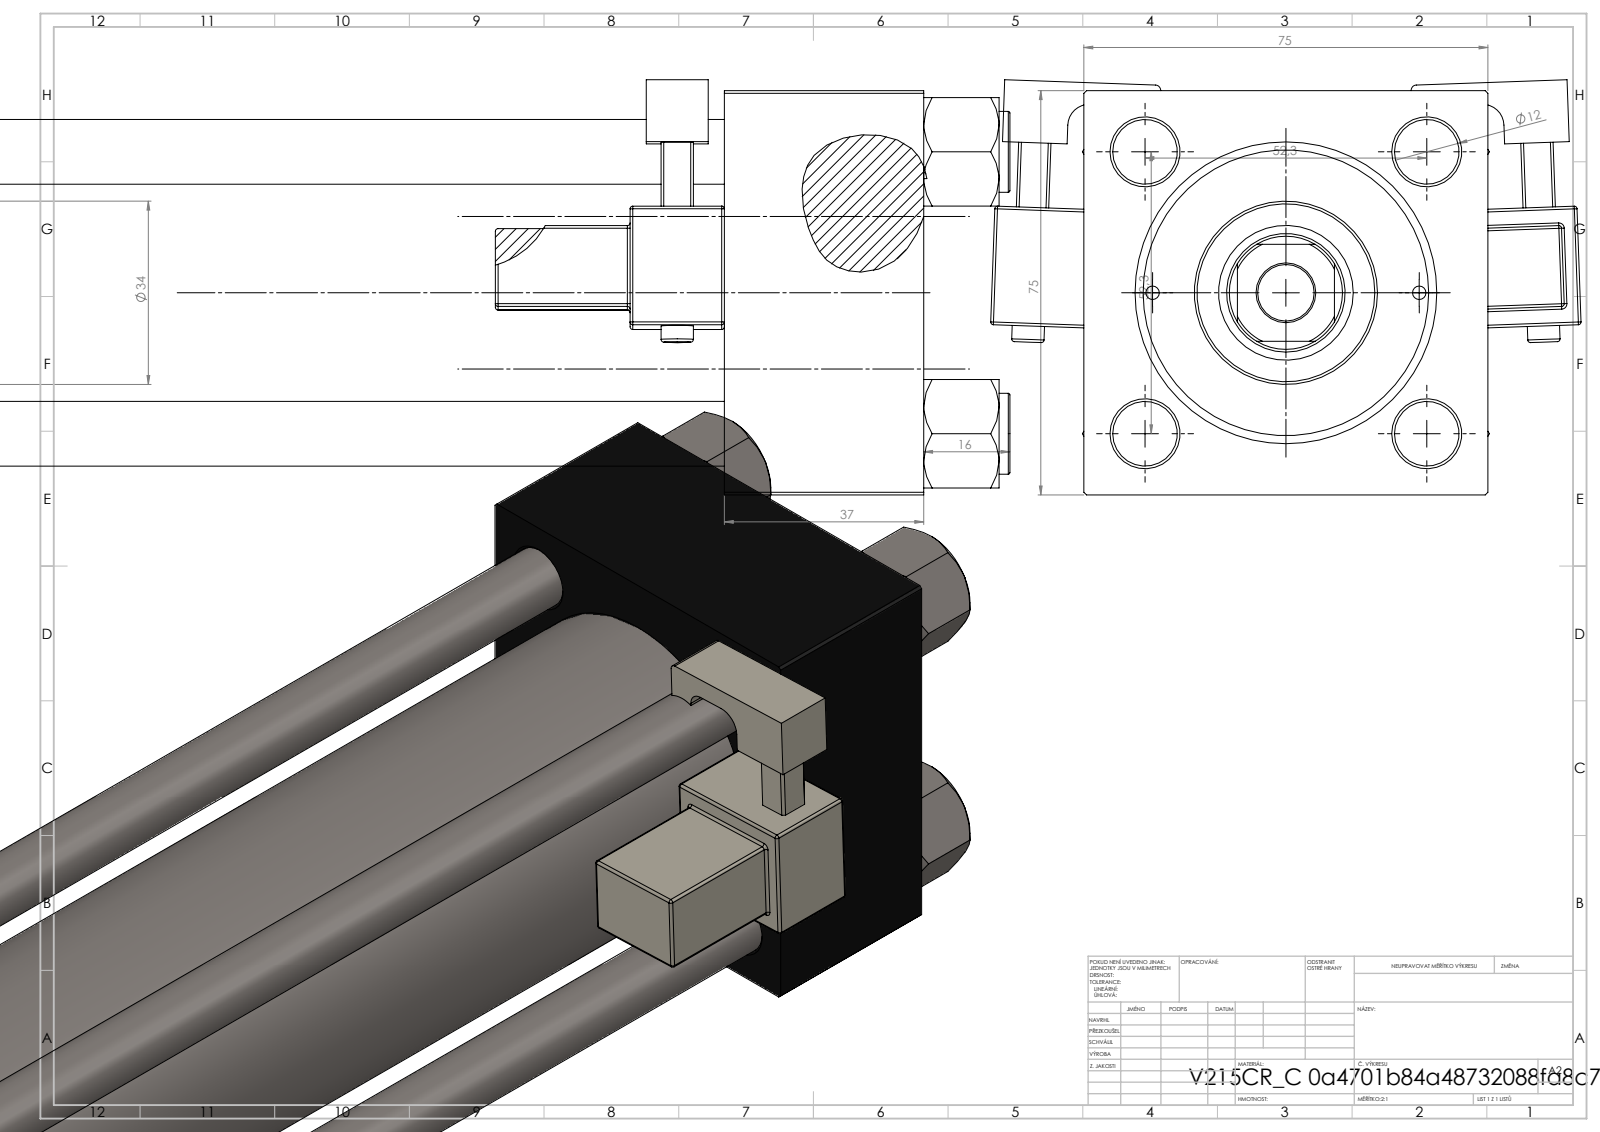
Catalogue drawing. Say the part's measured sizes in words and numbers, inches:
The part is named "V215CR_VCP_C; NUT_M5_C; V215_VC_A; V215CR_C_TYCINKA (+2 more)". Its 3-D file was written by "SolidWorks 2019 (CONFIG_CONTROL_DESIGN)". It is 13 solids with 1308 faces: 586 planar, 150 cylindrical and 572 other. Overall it measures 20.669 by 4.314 by 3.033 inches. Its volume is 69.45 cubic inches and its surface area 530.2 square inches. Round holes: 4 of diameter 0.472, 2 of diameter 0.098, 2 of diameter 0.276, 2 of diameter 0.825, 2 of diameter 1.181, 1 of diameter 0.413, 1 of diameter 0.866, 1 of diameter 0.984, 1 of diameter 1.614, 1 of diameter 1.969, 1 of diameter 2.087. Round bosses or shafts: 4 of diameter 0.591, 2 of diameter 0.236, 1 of diameter 2.205, 1 of diameter 1.339. Partial cylindrical surfaces (rounded edges, fillets, slot ends): 48 of radius 0.02, 2 of radius 0.039, 2 of radius 0.098, 2 of radius 0.157, 1 of radius 0.413. The main face-to-face distances are 2.953, 1.457, 19.055, 17.598, 16.732, 15.276, 2.323, 17.925, 16.469, 1.193. The hole center spacings are 1.031, 1.456, 2.059, 2.253, 0.974, 2.912, 1.949, 16.673.
